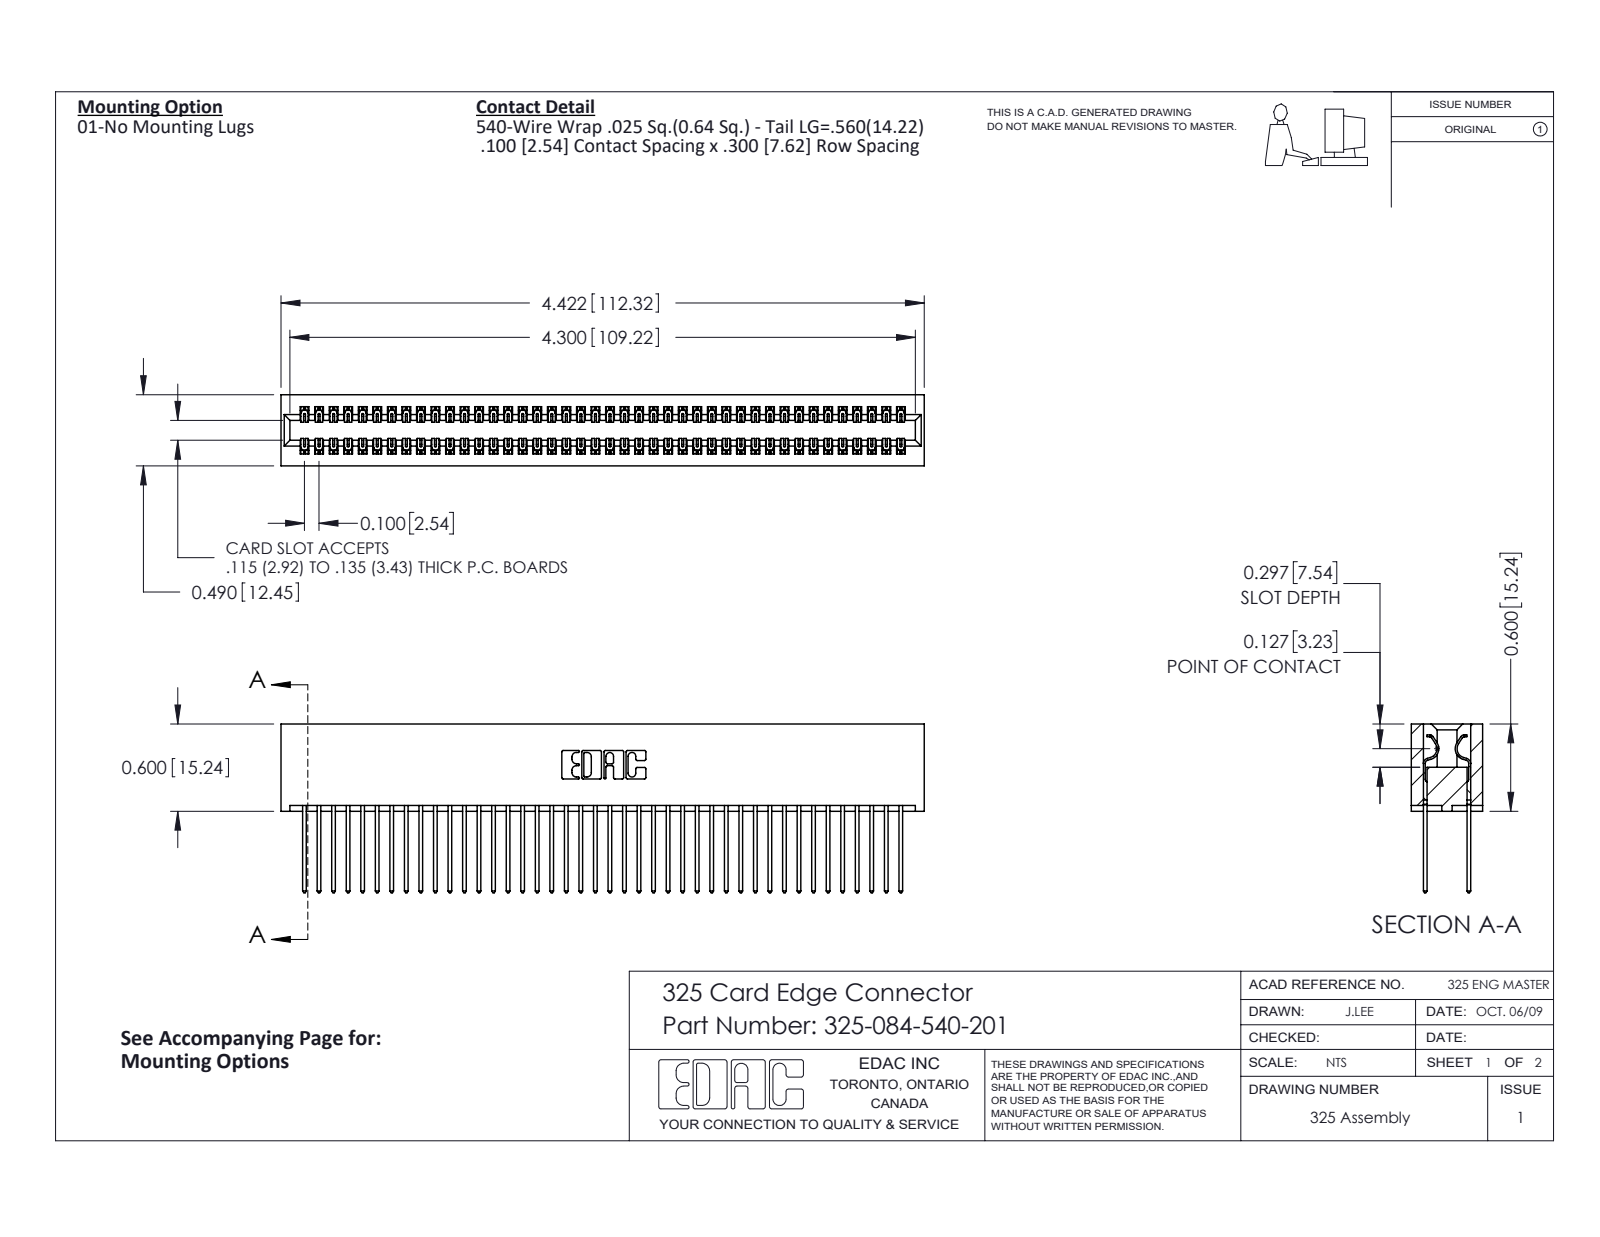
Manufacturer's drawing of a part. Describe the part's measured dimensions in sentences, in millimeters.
The part is named "325 Part_Lugless; 325-084-540-201; 325-292-001_325-293-140". Its 3-D file was written by "SolidWorks 2016 (CONFIG_CONTROL_DESIGN)". It is 85 solids with 4474 faces: 3090 planar, 1384 cylindrical and 0 other. Overall it measures 112.3 by 29.5 by 12.4 millimeters. Its volume is 15 400 cubic millimeters and its surface area 20 850 square millimeters. Partial cylindrical surfaces (rounded edges, fillets, slot ends): 126 of radius 0.2, 84 of radius 0.3, 22 of radius 0.3, 6 of radius 0.2, 6 of radius 0.8, 3 of radius 0.7, 2 of radius 0.4, 2 of radius 0.6. The main face-to-face distances are 2.1, 10.3, 7.6, 2.7, 9.7, 0.6, 8.3, 12.4, 7, 14.2.
